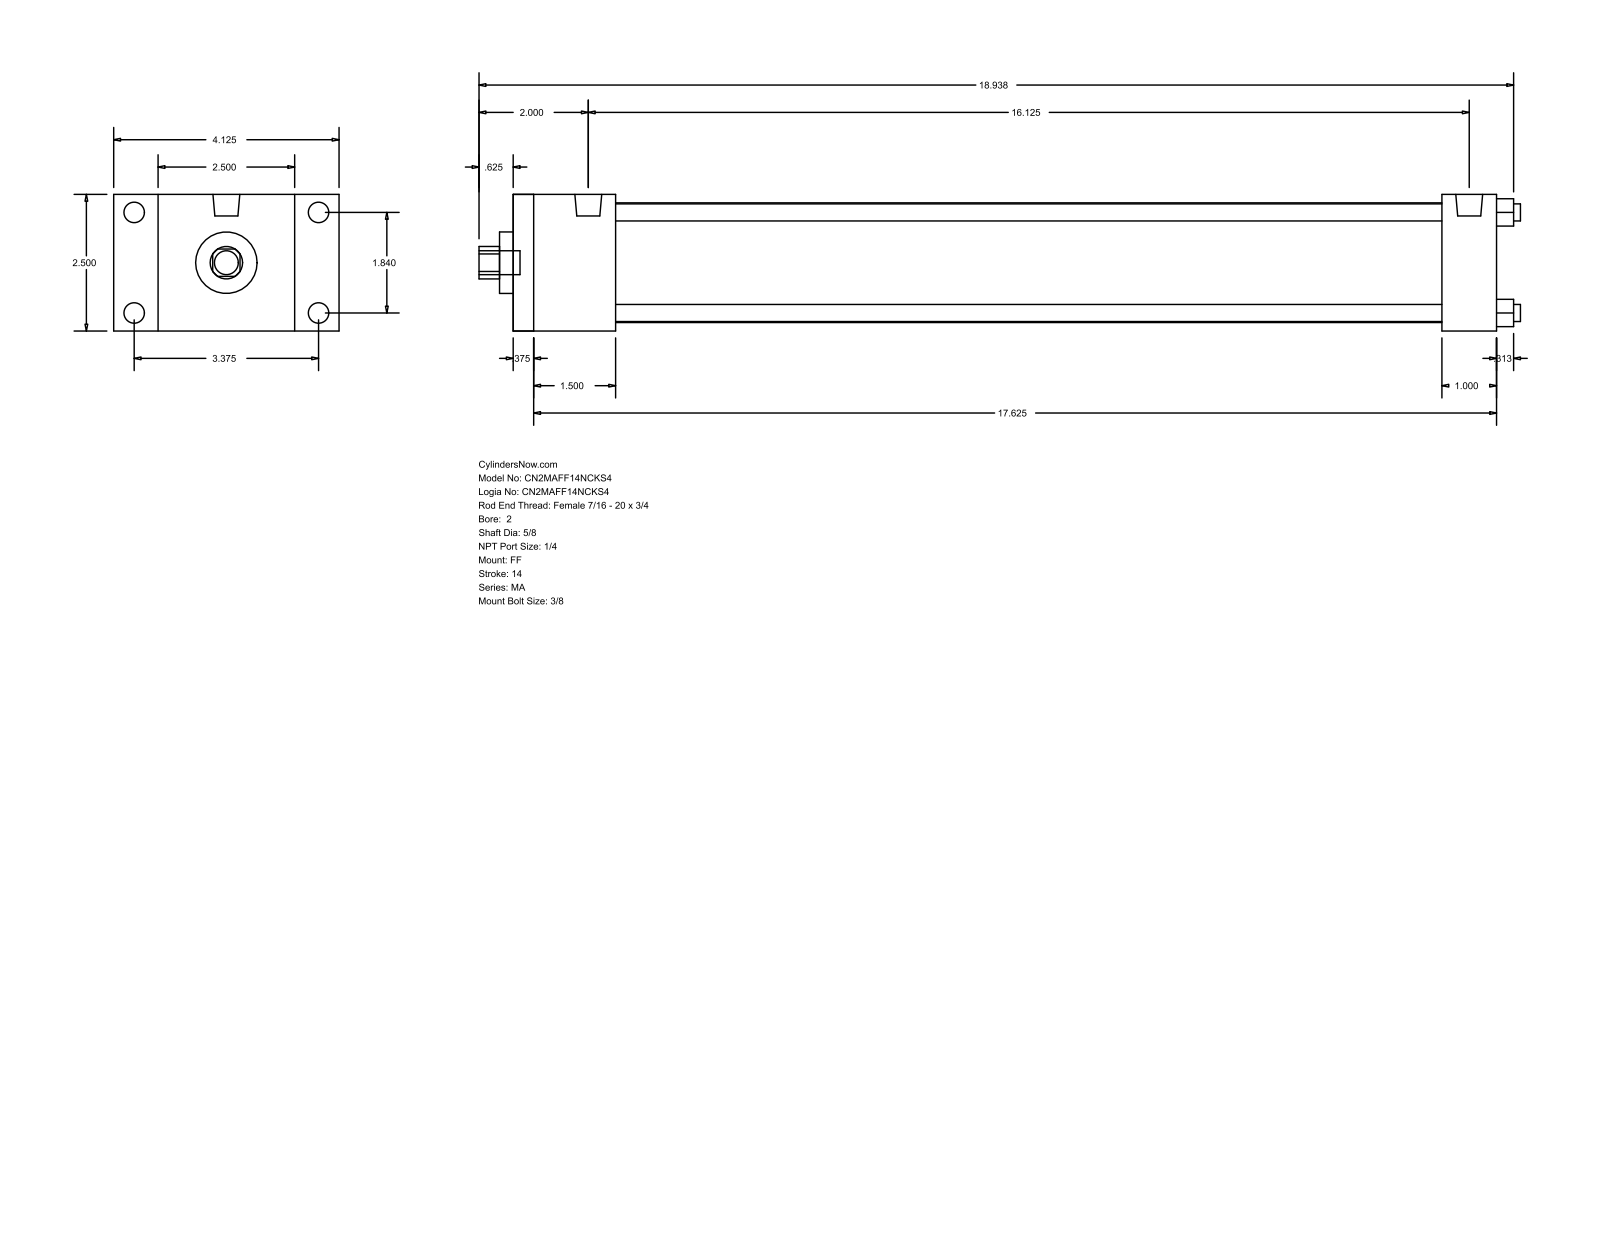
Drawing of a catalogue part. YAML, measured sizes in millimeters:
part_name: "MA_FF__0200_0.625"
step_written_by: "GSSL Pune (CONFIG_CONTROL_DESIGN)"
units: millimeters
bodies: {solids: 0, faces: 92, planar: 64, cylindrical: 28, other: 0}
overall_size: [484.19, 104.78, 63.5]
round_holes:
  - {diameter: 7.94, count: 4}
  - {diameter: 15.88, count: 1}
  - {diameter: 28.57, count: 1}
  - {diameter: 55.63, count: 1}
round_bosses_or_shafts:
  - {diameter: 9.53, count: 4}
  - {diameter: 7.94, count: 4}
  - {diameter: 12.49, count: 2}
  - {diameter: 11.11, count: 1}
partial_cylinders:
  - {radius: 7.54, count: 1}
face_to_face_distances: [63.5, 457.19, 9.52, 447.67, 38.1, 47.62, 431.8, 422.28, 384.18, 409.57]
hole_center_spacings: [33.05, 46.74, 66.1]
